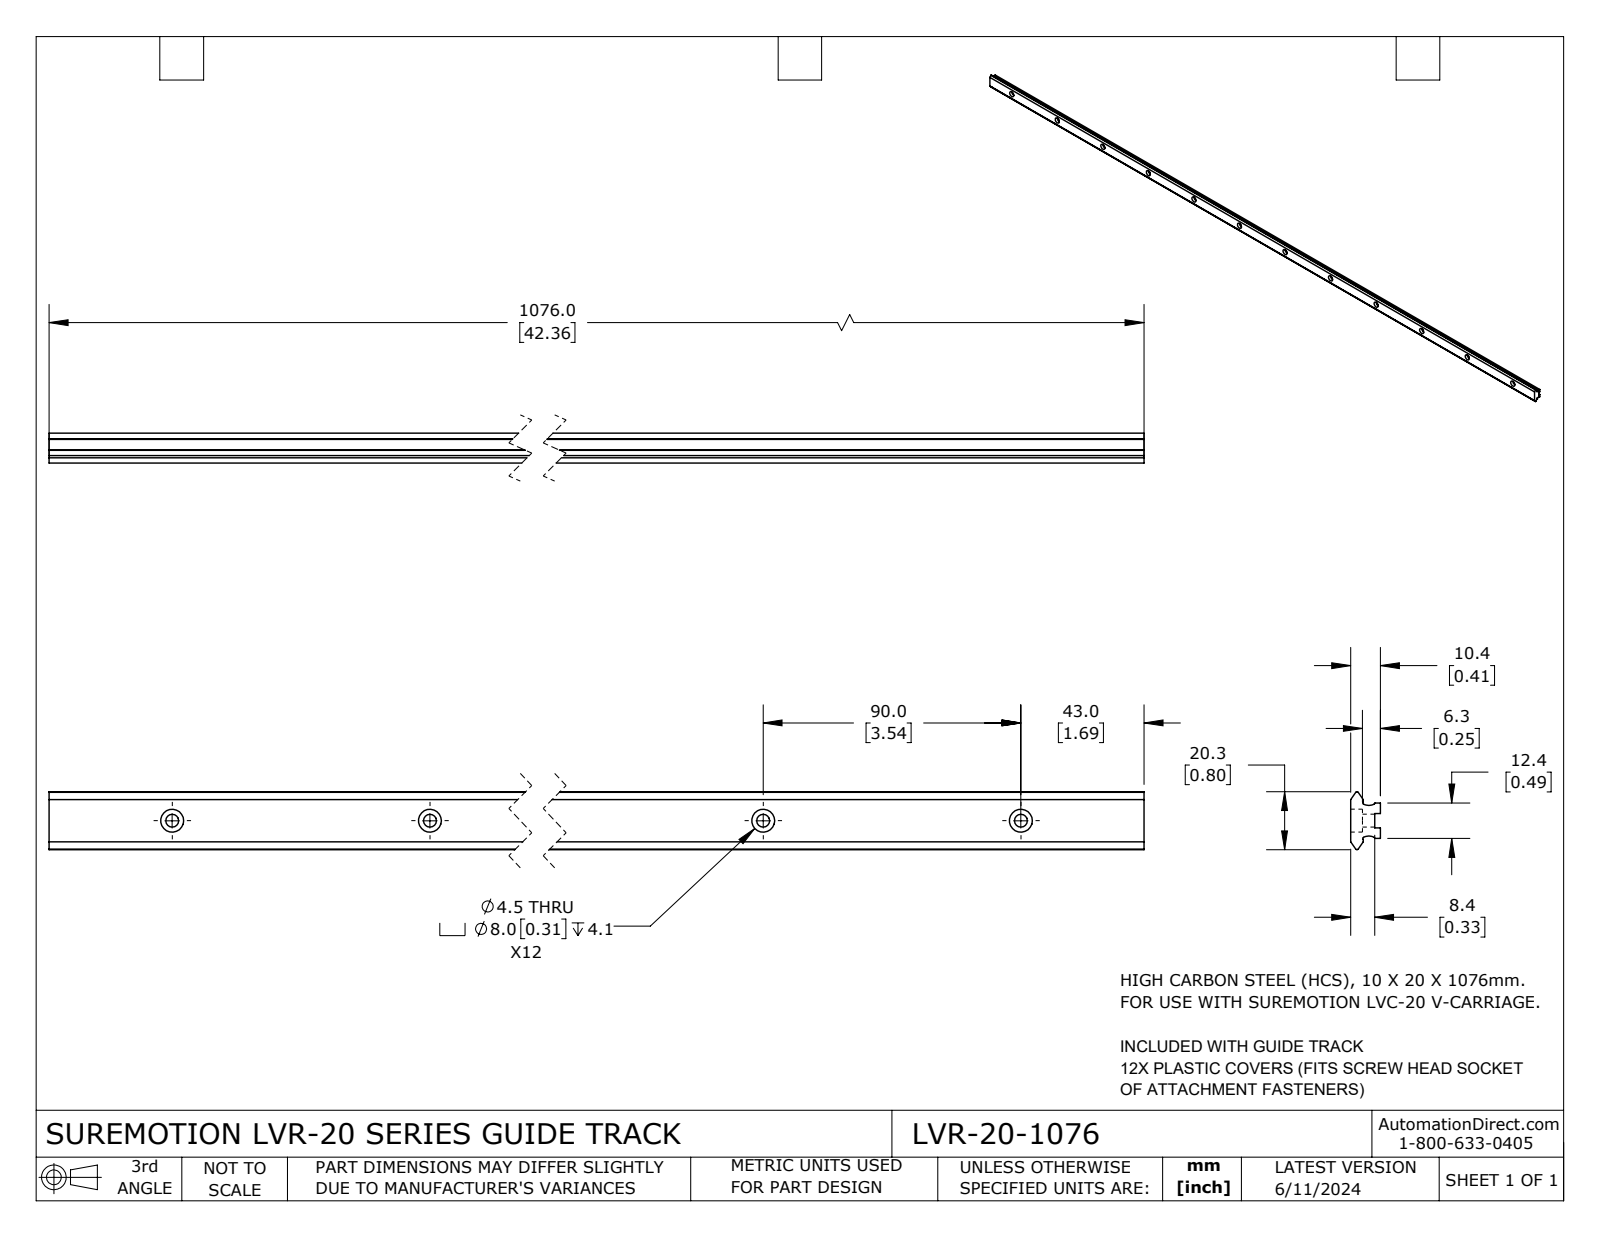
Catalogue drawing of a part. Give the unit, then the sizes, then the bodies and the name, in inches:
Units: inches
Overall size (bounding box): 42.362 × 0.798 × 0.41
Round holes (diameter × count): ⌀0.177 ×12, ⌀0.315 ×12
Partial cylindrical surfaces — rounded edges, fillets, slot ends (radius × count): R0.016 ×4, R0.02 ×2, R0.151 ×2
Main face-to-face distances: 0.41, 0.079, 0.331, 0.146, 0.343, 0.475, 0.474, 0.197, 0.488, 0.236
Hole centre spacings: 3.543, 7.087, 10.63, 14.173, 17.717, 21.26, 24.803, 28.346
Volume: 8.825 in³ · Surface area: 105.5 in²
Bodies: 1 solid, 86 faces (28 planar, 58 cylindrical, 0 other)
Part name (STEP PRODUCT): LVR-20-1076
STEP written by: SolidWorks 2023 (CONFIG_CONTROL_DESIGN)
